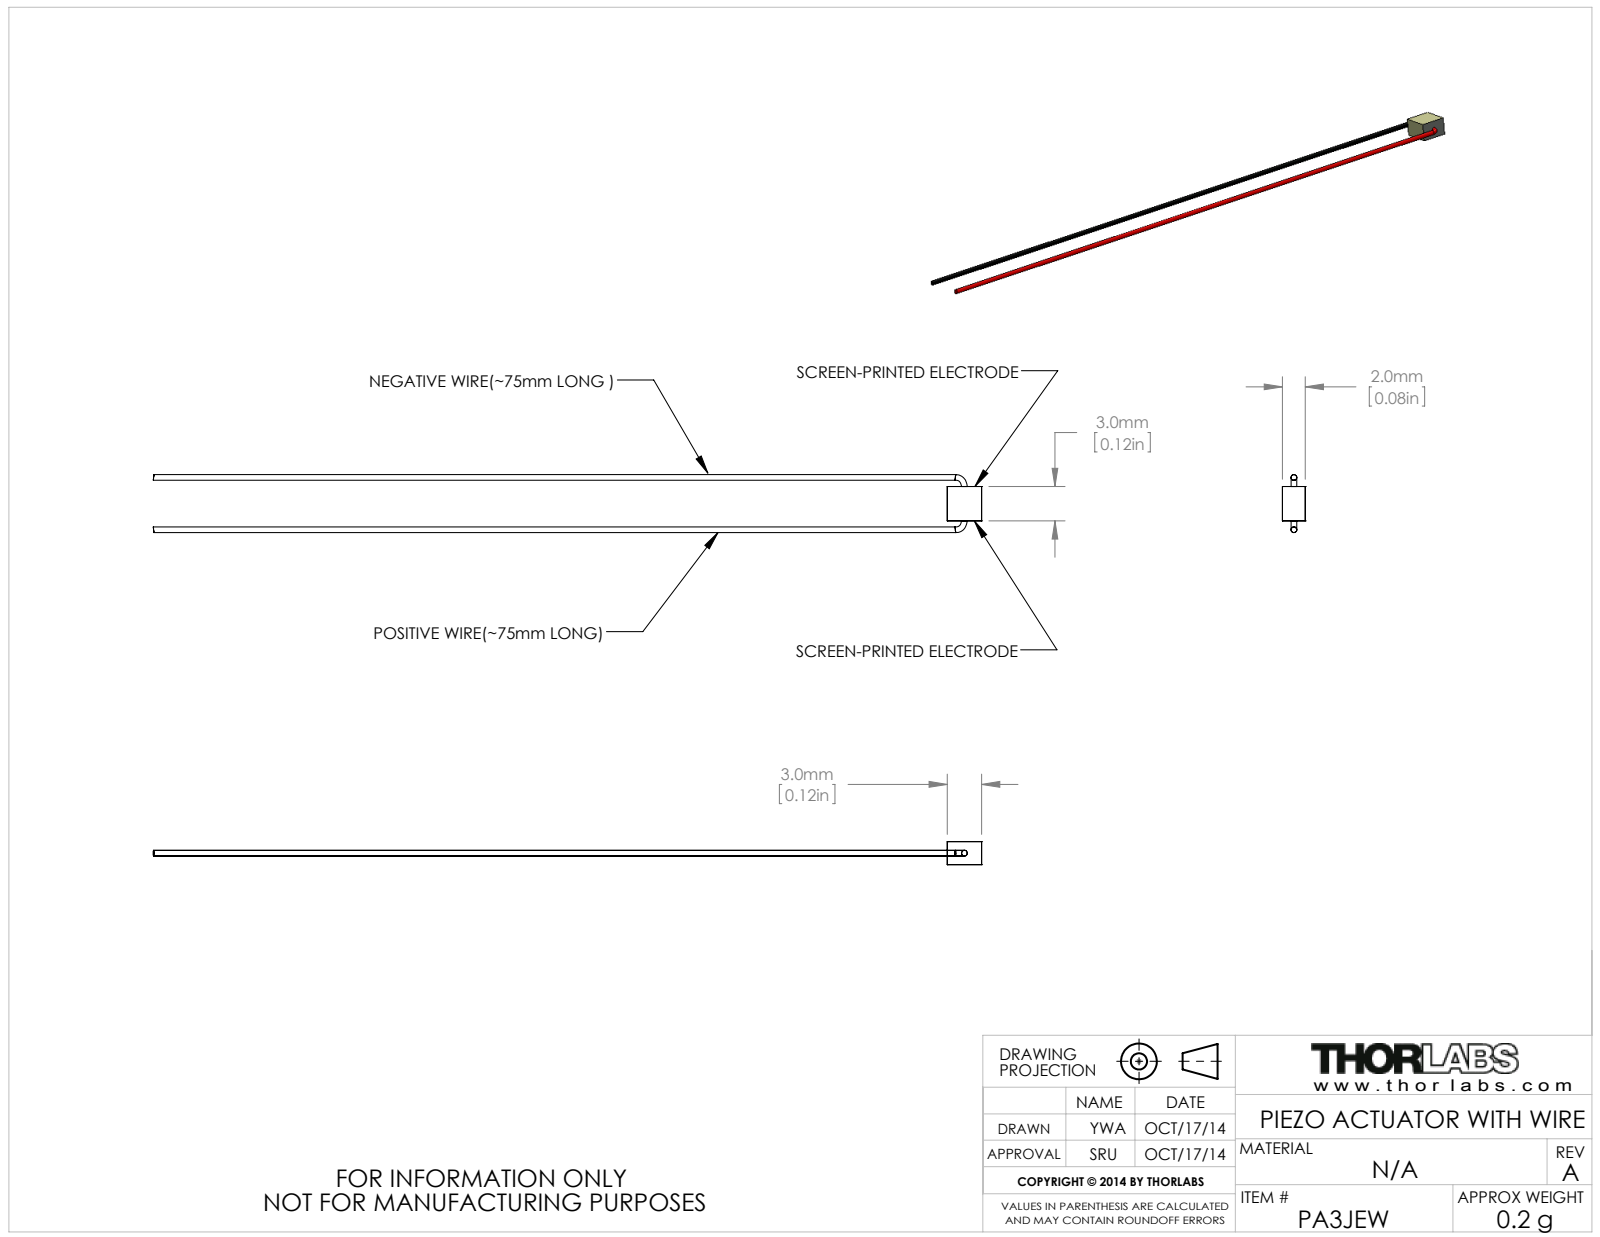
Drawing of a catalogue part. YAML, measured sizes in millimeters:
part_name: "PA3JEW"
step_written_by: "SolidWorks 2012 (AUTOMOTIVE_DESIGN)"
units: millimeters
bodies: {solids: 1, faces: 16, planar: 8, cylindrical: 0, other: 8}
overall_size: [72.33, 5.06, 2]
volume: 46
surface_area: 265
face_to_face_distances: [3, 2]
